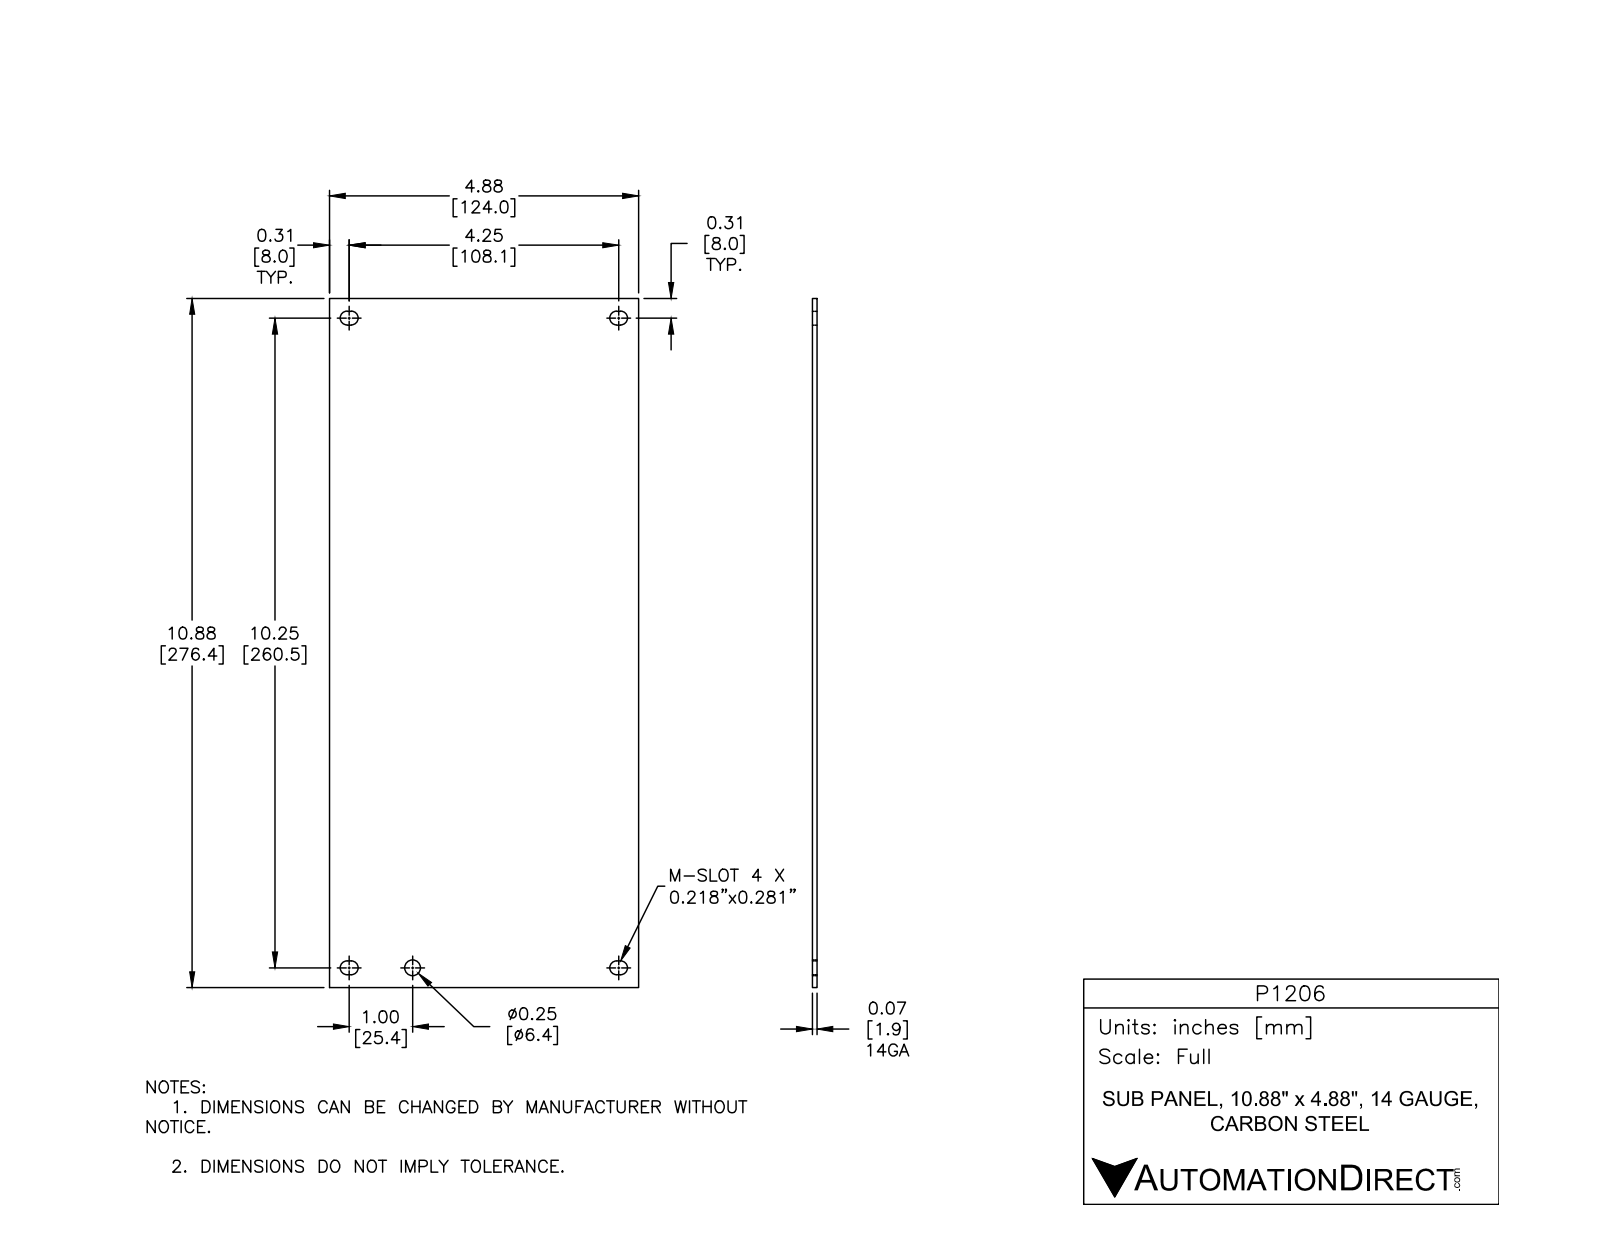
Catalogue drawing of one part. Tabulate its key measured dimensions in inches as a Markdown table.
| quantity | value |
| --- | --- |
| part name | P1206 |
| STEP written by | Autodesk Inventor 2012 (AUTOMOTIVE_DESIGN) |
| units | inches |
| bodies | 1 solid, 23 faces (14 planar, 9 cylindrical, 0 other) |
| overall size | 10.88 × 4.88 × 0.074 |
| volume | 3.91 in³ |
| surface area | 108.3 in² |
| round holes (diameter × count) | 0.25 × 1 |
| partial cylindrical surfaces (radius × count) | 0.109 × 8 |
| main face-to-face distances | 0.074, 4.88, 10.88, 0.204, 10.676, 0.422, 10.458, 0.218, 10.254, 10.472 |
